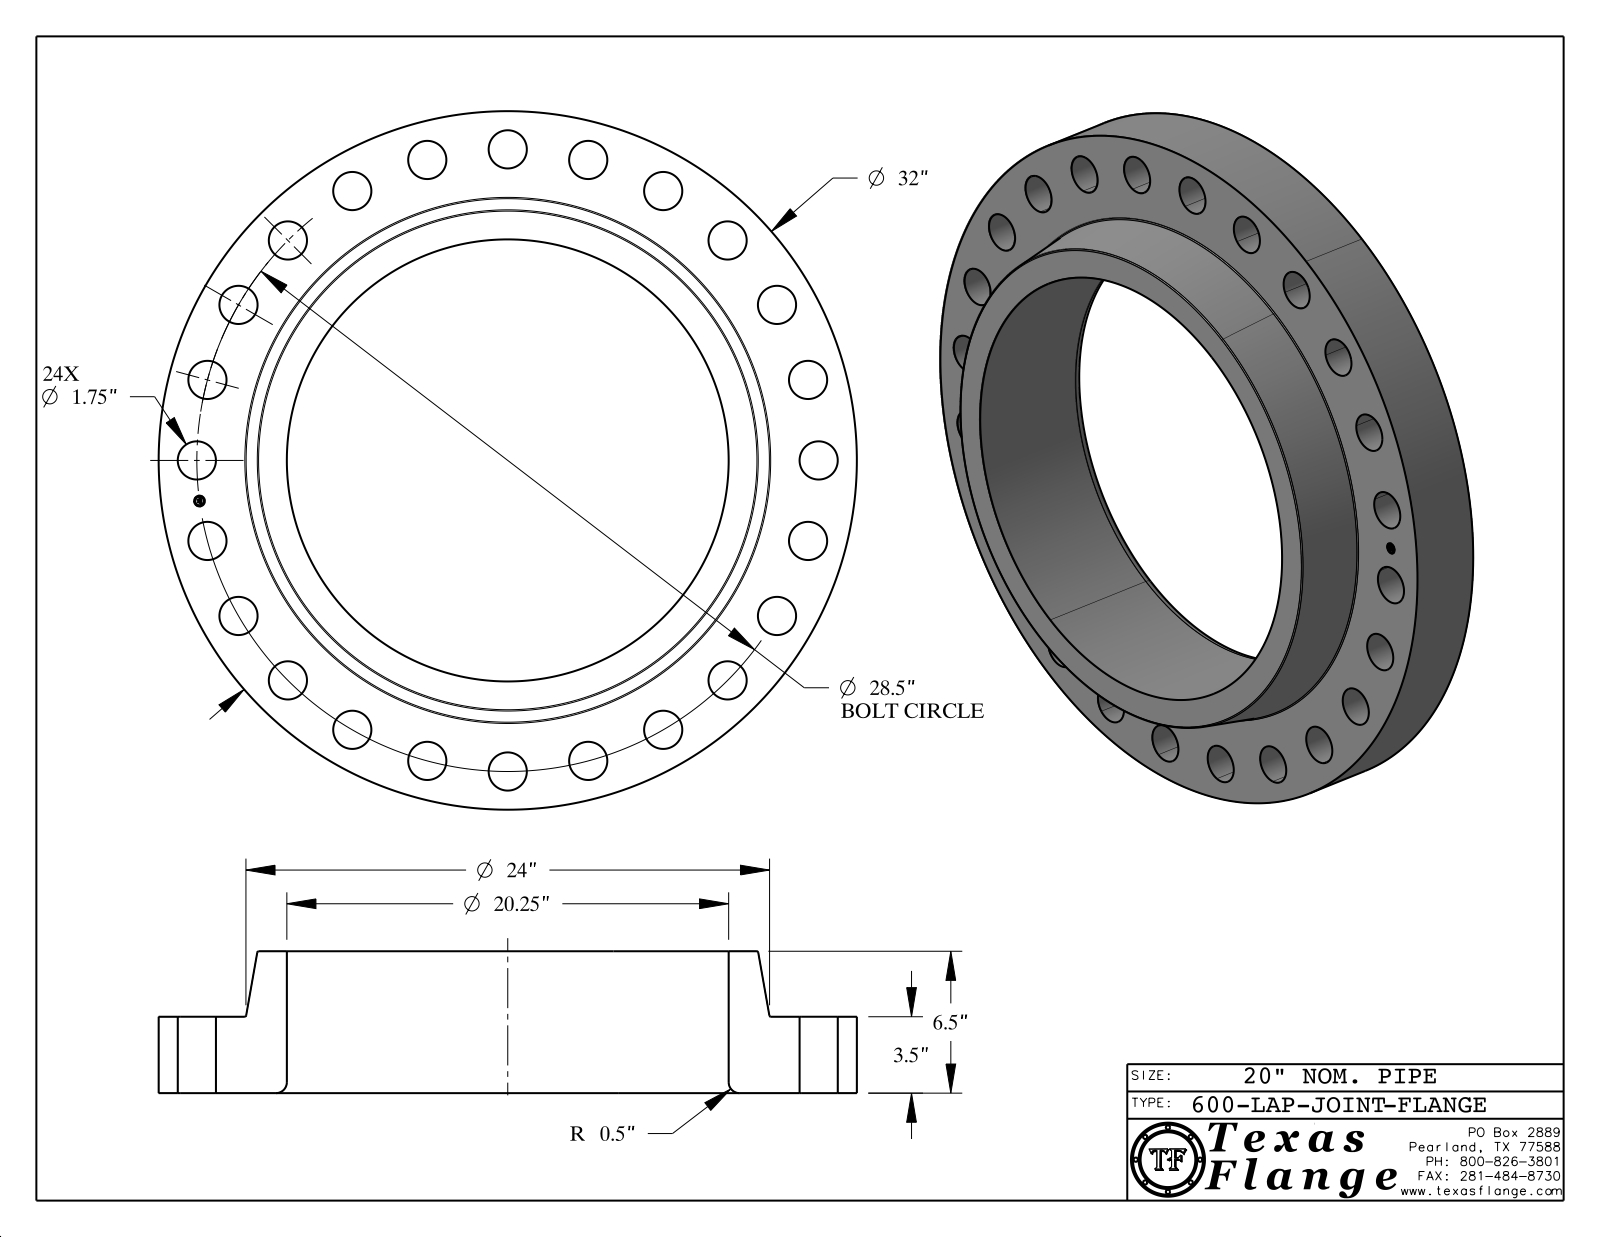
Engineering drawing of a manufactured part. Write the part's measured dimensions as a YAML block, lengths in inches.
part_name: "600-LAP-JOINT FLANGE"
step_written_by: "CATIA V5 STEP AP214 (AUTOMOTIVE_DESIGN)"
units: inches
bodies: {solids: 1, faces: 448, planar: 368, cylindrical: 72, other: 8}
overall_size: [32, 32, 6.5]
volume: 1814
surface_area: 2246
round_holes:
  - {diameter: 1.75, count: 24}
  - {diameter: 0.495, count: 1}
  - {diameter: 20.25, count: 1}
round_bosses_or_shafts:
  - {diameter: 0.03, count: 8}
  - {diameter: 32, count: 1}
  - {diameter: 0.39, count: 1}
face_to_face_distances: [3.5, 6.5, 3, 0.015, 3.485, 3.015, 0.148, 0.145, 0.027, 0.096]
hole_center_spacings: [14.25, 3.72, 7.376, 24.682, 26.331, 27.529, 20.153, 10.907]
